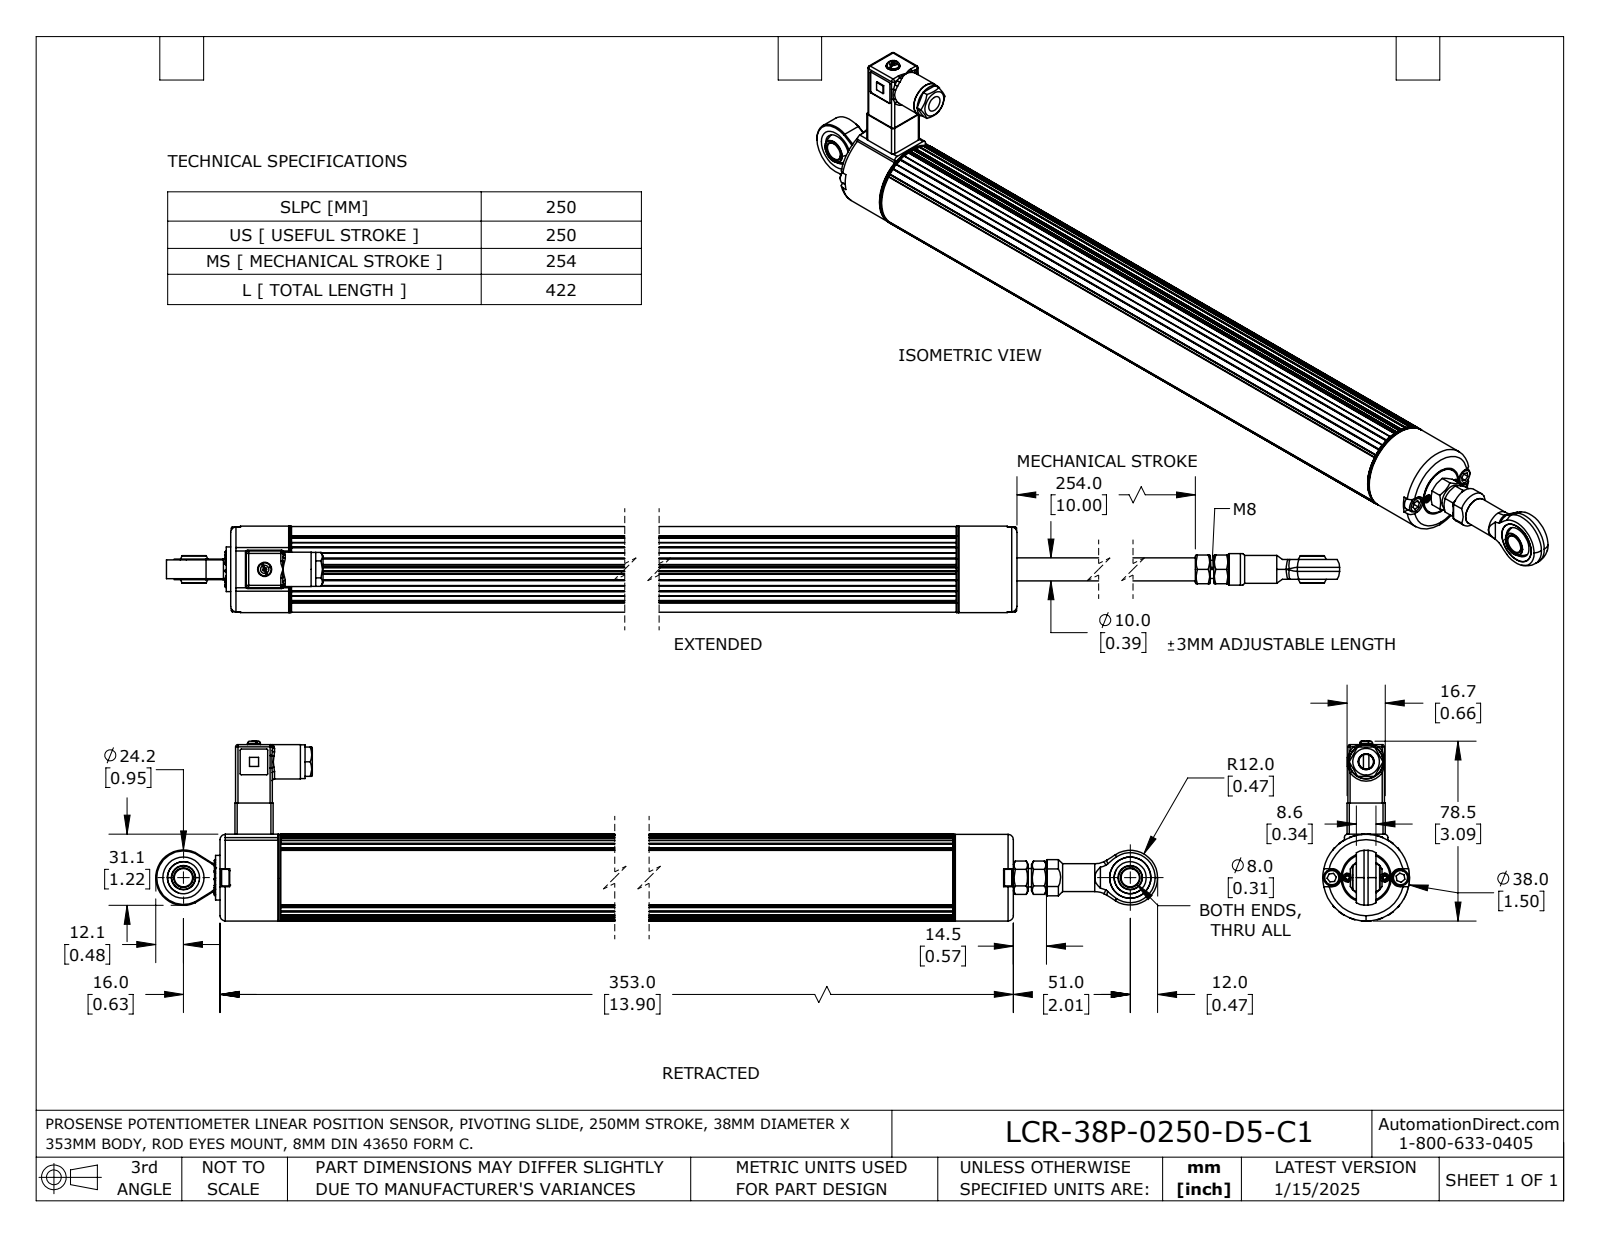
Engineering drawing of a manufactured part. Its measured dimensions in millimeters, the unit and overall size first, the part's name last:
Units: millimetres
Overall size (bounding box): 444 × 78.6 × 37.8
Round holes (diameter × count): ⌀2.6 ×6, ⌀2.3 ×4, ⌀8 ×3, ⌀14 ×3, ⌀2.4 ×2, ⌀2.5 ×2, ⌀2.8 ×2, ⌀3.4 ×2, ⌀3.9 ×2, ⌀4.2 ×2, ⌀2 ×1, ⌀3 ×1
Round bosses / shafts (diameter × count): ⌀1.6 ×6, ⌀7.2 ×4, ⌀3.8 ×4, ⌀12.2 ×2, ⌀2 ×2, ⌀37.8 ×1, ⌀20.9 ×1, ⌀19.5 ×1
Partial cylindrical surfaces — rounded edges, fillets, slot ends (radius × count): R0.2 ×32, R1 ×20, R0.5 ×12, R0.4 ×6, R0.3 ×2, R1.5 ×2, R2.1 ×2, R2.5 ×2
Main face-to-face distances: 300, 26.5, 326.5, 0.8, 1.1, 15.5, 15.2, 0.4, 16.4, 3.5
Hole centre spacings: 16.1, 1.9, 16.1, 6.7, 6.8, 7.2, 8.2, 10
Volume: 409 200 mm³ · Surface area: 77 290 mm²
Bodies: 11 solids, 657 faces (295 planar, 210 cylindrical, 152 other)
Part name (STEP PRODUCT): LCR-38P-0250-D5-C1
STEP written by: SolidWorks 2023 (AUTOMOTIVE_DESIGN)
